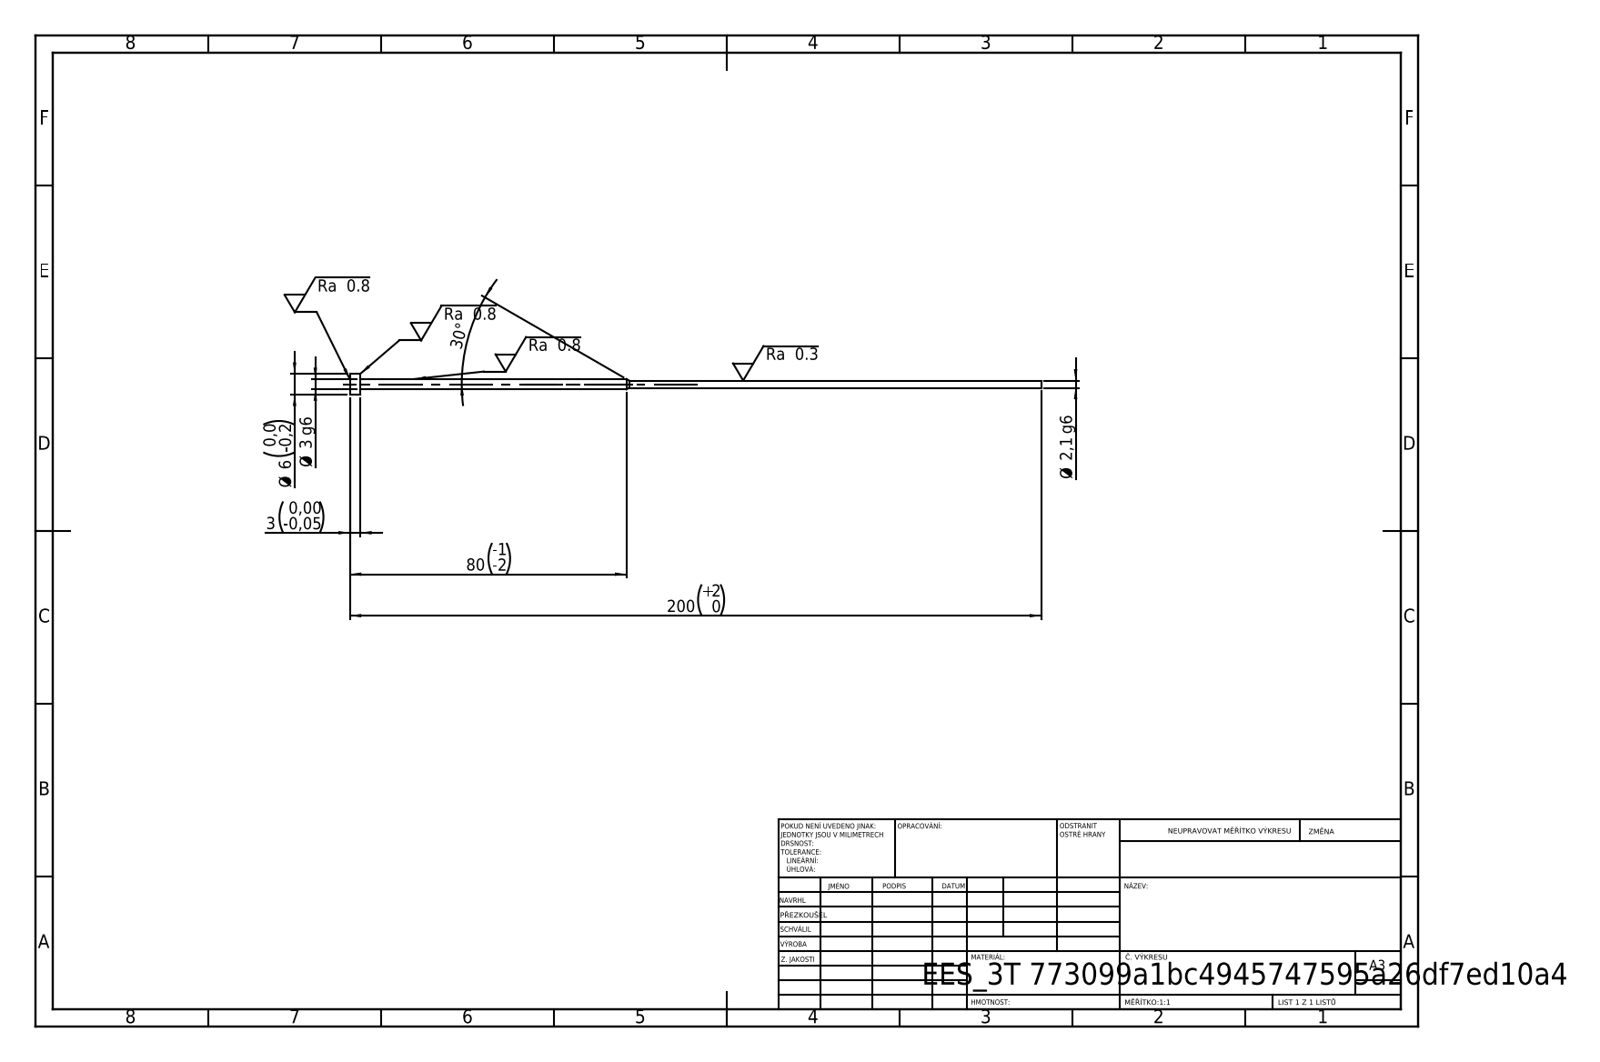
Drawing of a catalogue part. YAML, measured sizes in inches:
step_written_by: "SolidWorks 2019 (CONFIG_CONTROL_DESIGN)"
units: inches
bodies: {solids: 1, faces: 11, planar: 3, cylindrical: 6, other: 2}
overall_size: [7.874, 0.236, 0.236]
volume: 0.064
surface_area: 2.525
round_bosses_or_shafts:
  - {diameter: 0.236, count: 1}
  - {diameter: 0.118, count: 1}
  - {diameter: 0.083, count: 1}
face_to_face_distances: [0.118, 7.756, 7.874]
